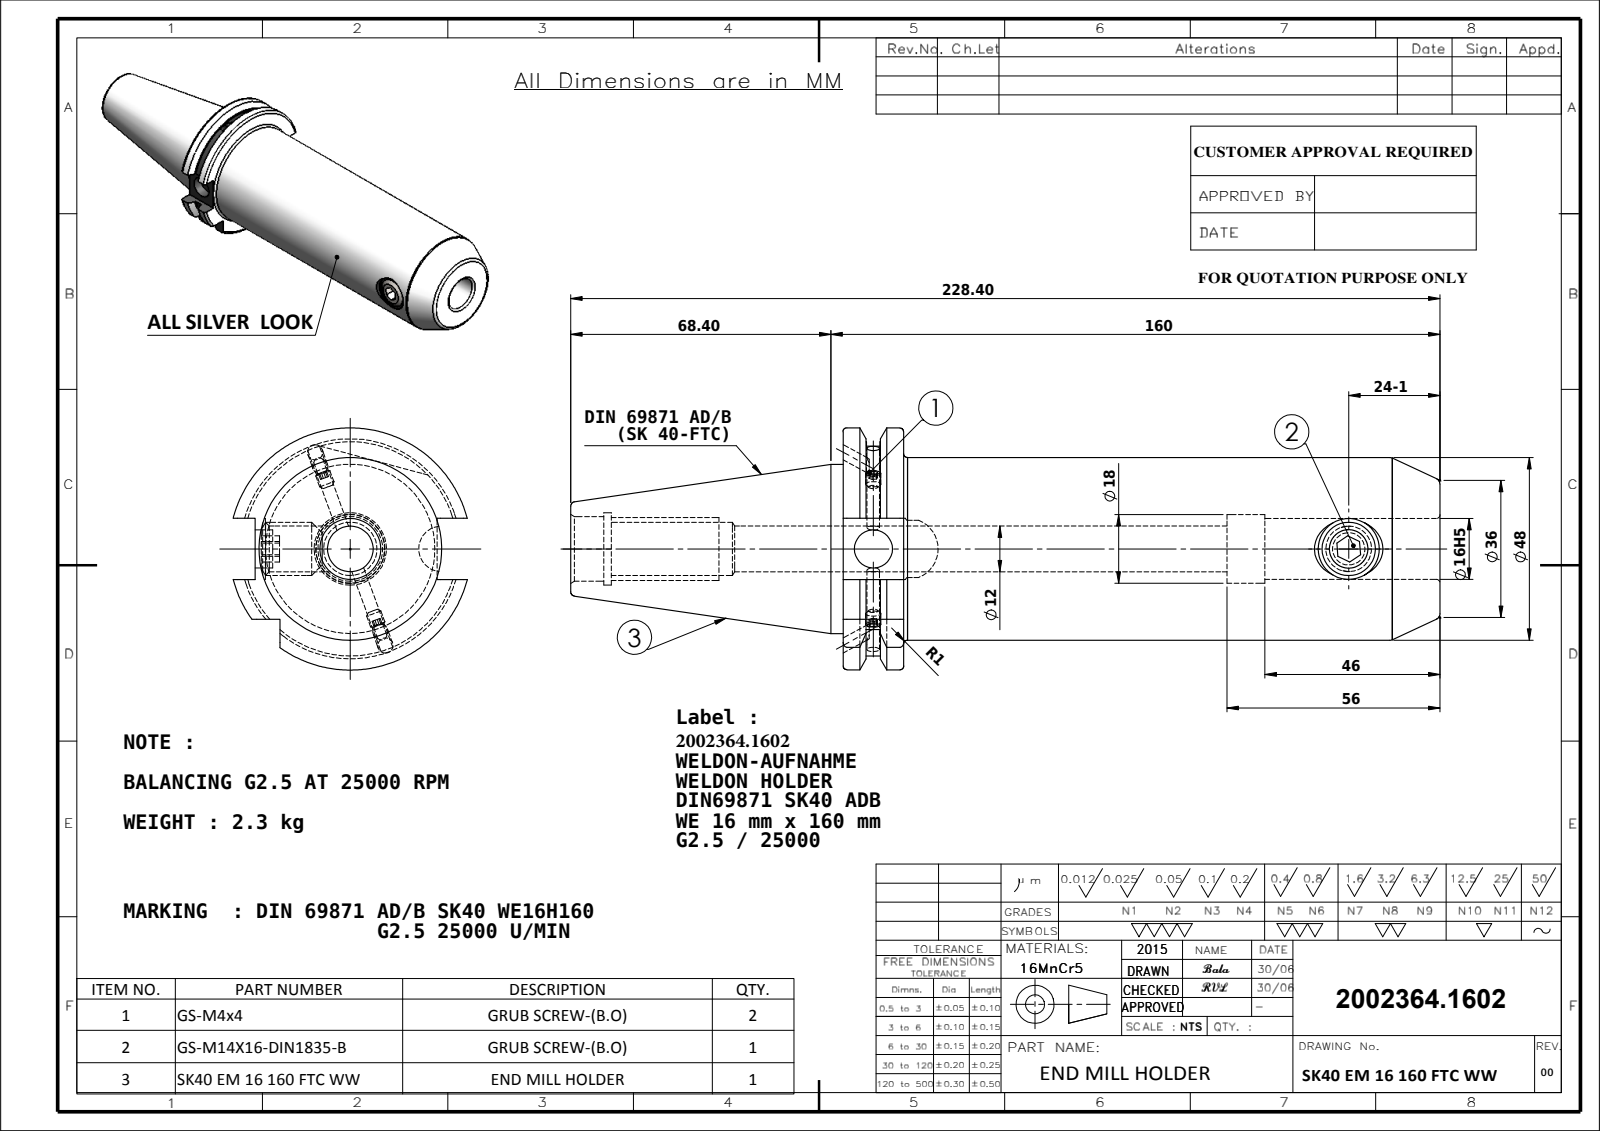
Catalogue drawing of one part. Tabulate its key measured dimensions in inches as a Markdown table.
| quantity | value |
| --- | --- |
| part name | SK40 EM 16 160 FTC WW; Copy of M4X4_DIN 913 - M4 x 4-N; 91406-WE716160; M14X16_ISO 4026 - M12 x 12-N |
| STEP written by | SolidWorks 2009 (CONFIG_CONTROL_DESIGN) |
| units | inches |
| bodies | 4 solids, 161 faces (59 planar, 45 cylindrical, 57 other) |
| overall size | 8.992 × 2.502 × 2.42 |
| volume | 20.02 in³ |
| surface area | 76.22 in² |
| round holes (diameter × count) | 0.472 × 2, 0.63 × 2, 0.13 × 1, 0.394 × 1, 0.551 × 1, 0.669 × 1, 0.709 × 1, 0.748 × 1 |
| round bosses / shafts (diameter × count) | 0.157 × 2, 1.89 × 1, 1.75 × 1, 0.551 × 1 |
| partial cylindrical surfaces (radius × count) | 0.317 × 1, 1.107 × 1, 1.251 × 1 |
| main face-to-face distances | 0.626, 6.173, 5.547, 0.634, 1.882, 3.969, 3.343, 2.205, 2.819, 3.445 |
| hole center spacings | 4.915 |
